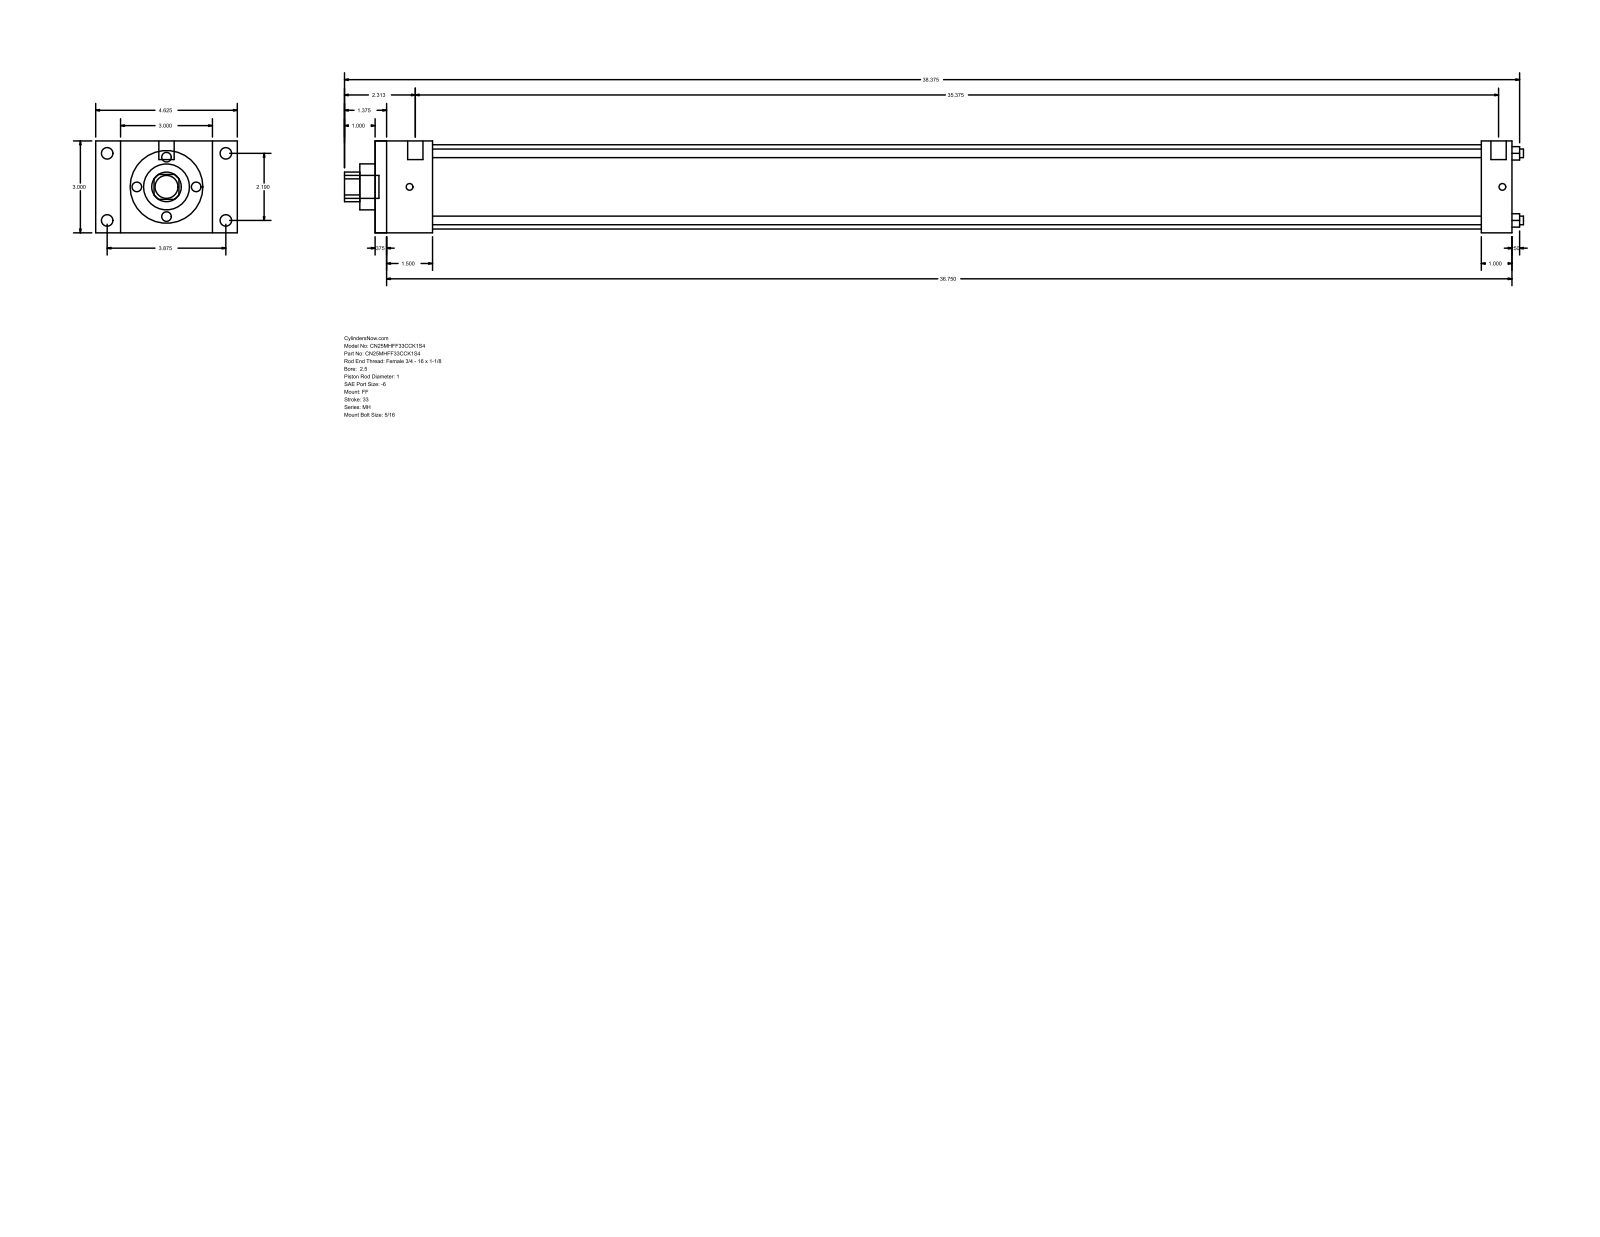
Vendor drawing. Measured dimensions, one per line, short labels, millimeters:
name: MH_FF__0250_1
written by: GSSL Pune (CONFIG_CONTROL_DESIGN)
unit: mm
bodies: 0 solids, 92 faces (64 planar, 28 cylindrical, 0 other)
size: 977.9 × 117.47 × 76.2
holes: 4× ⌀7.14, 1× ⌀25.4, 1× ⌀38.1, 1× ⌀69.85
bosses: 4× ⌀9.53, 4× ⌀5.56, 2× ⌀12.7, 1× ⌀19.05
rounds: 1× R12.29
face distances: 76.2, 942.98, 9.52, 933.46, 25.4, 47.63, 917.58, 38.11, 908.06, 869.95
hole spacings: 39.33, 55.62, 78.66
